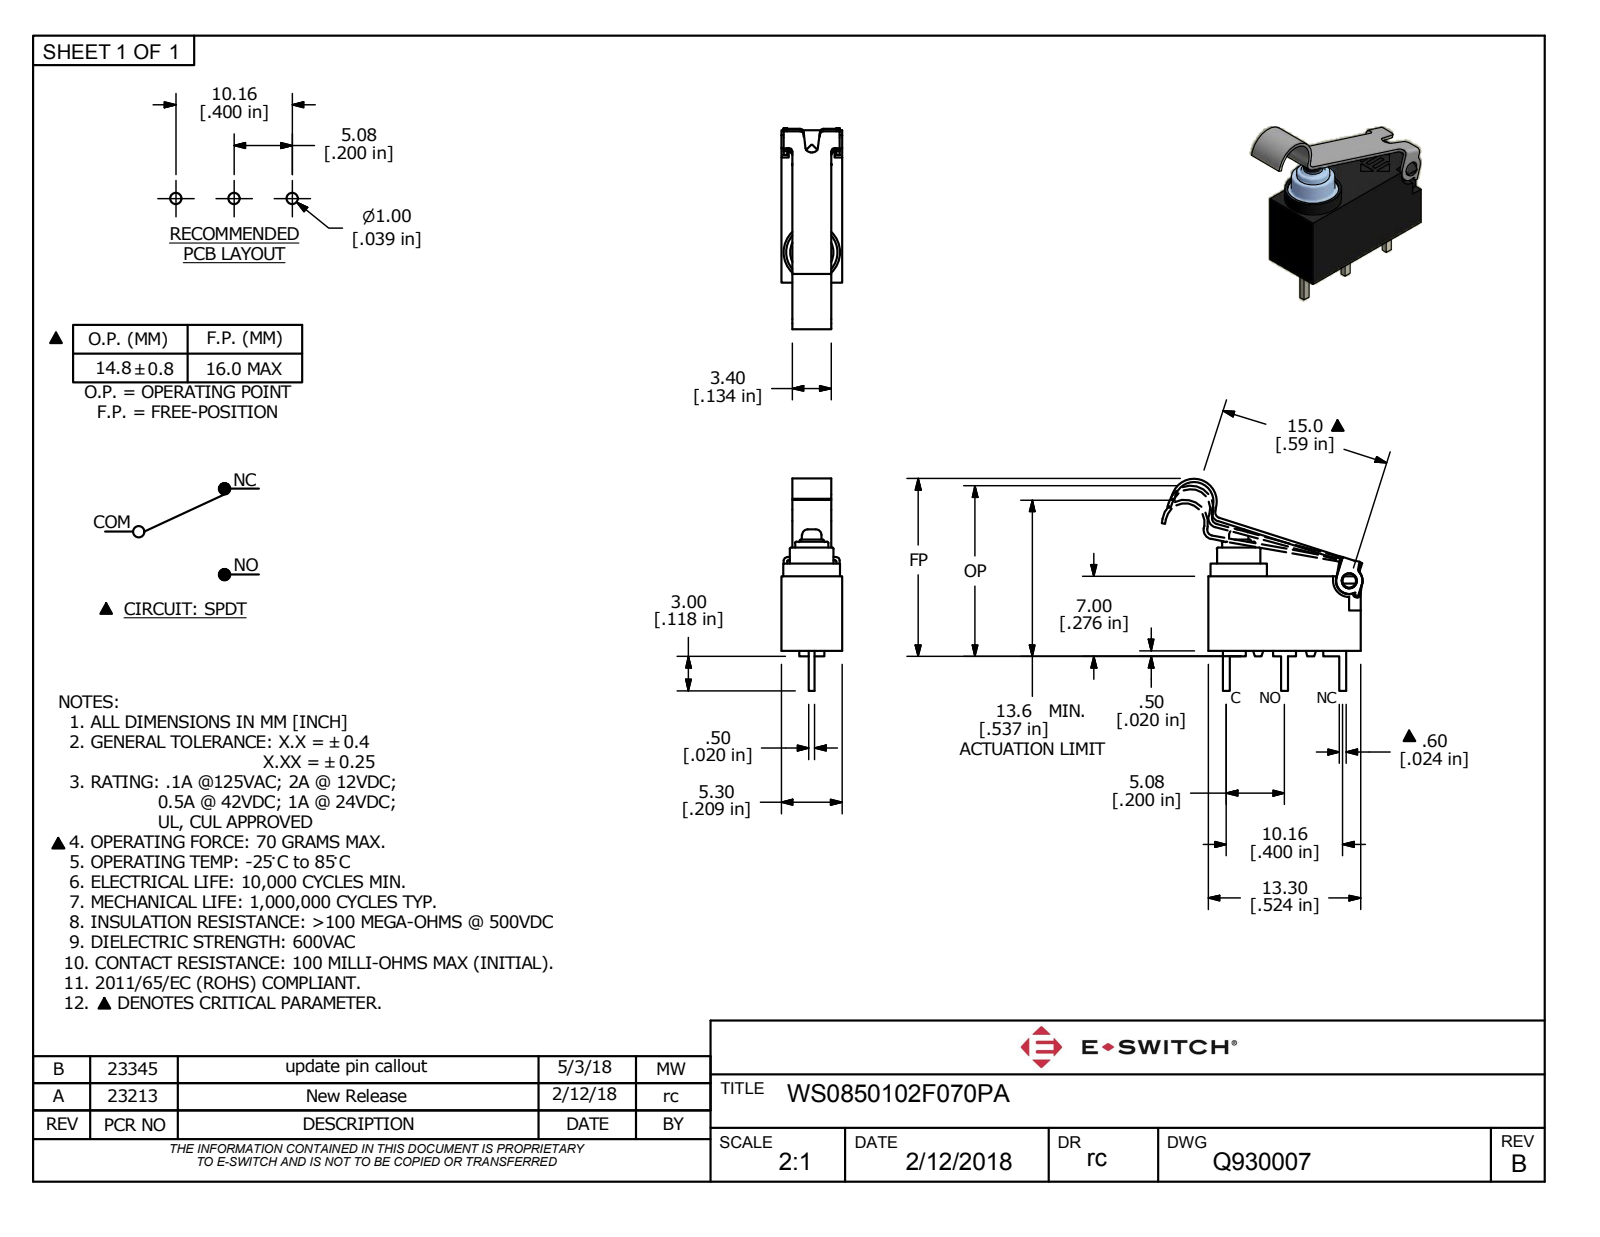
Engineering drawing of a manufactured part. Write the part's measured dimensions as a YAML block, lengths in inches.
part_name: "WS0850102F070PA"
step_written_by: "Autodesk Inventor 2012 (CONFIG_CONTROL_DESIGN)"
units: inches
bodies: {solids: 2, faces: 177, planar: 117, cylindrical: 53, other: 7}
overall_size: [0.729, 0.658, 0.209]
volume: 0.032
surface_area: 1.006
round_holes:
  - {diameter: 0.051, count: 1}
  - {diameter: 0.177, count: 1}
round_bosses_or_shafts:
  - {diameter: 0.195, count: 1}
  - {diameter: 0.15, count: 1}
  - {diameter: 0.114, count: 1}
  - {diameter: 0.067, count: 1}
partial_cylinders:
  - {radius: 0.012, count: 6}
  - {radius: 0.004, count: 2}
  - {radius: 0.01, count: 2}
  - {radius: 0.018, count: 2}
  - {radius: 0.02, count: 1}
  - {radius: 0.024, count: 1}
  - {radius: 0.031, count: 1}
  - {radius: 0.045, count: 1}
face_to_face_distances: [0.209, 0.256, 0.524, 0.094, 0.02, 0.114, 0.018, 0.163, 0.024, 0.252]
